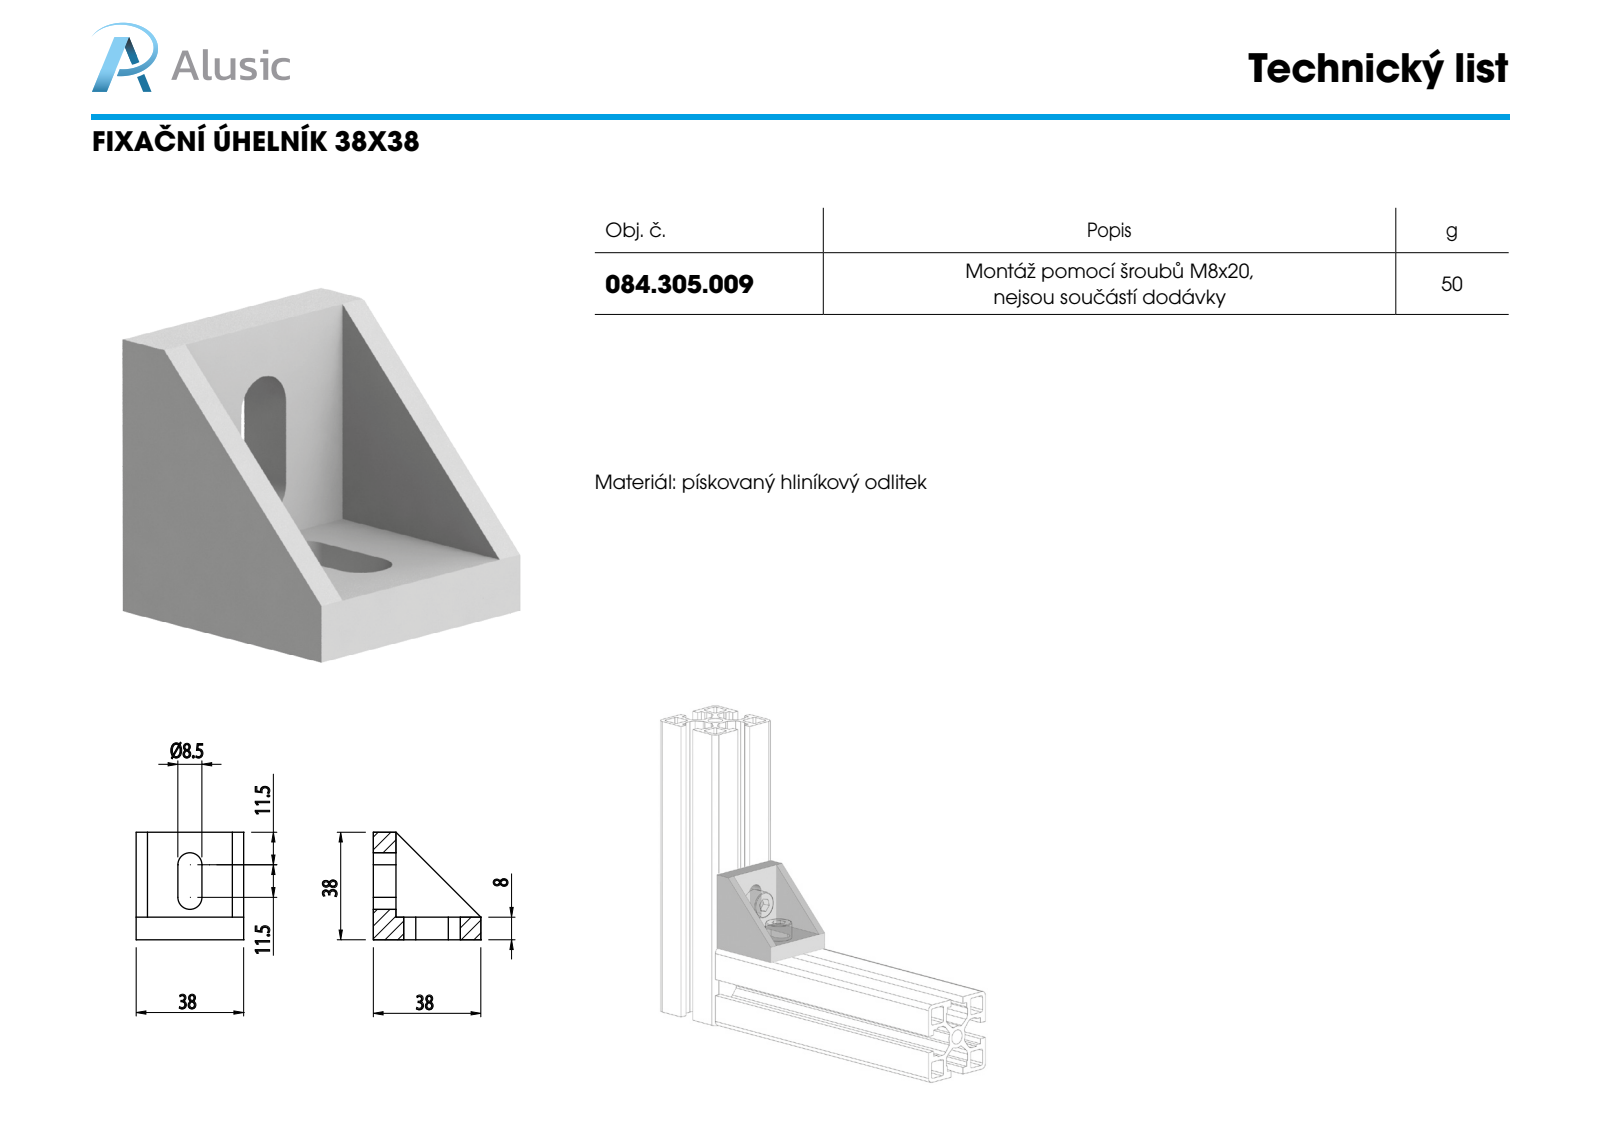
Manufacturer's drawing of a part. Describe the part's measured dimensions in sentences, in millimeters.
The part is named "084.305.009". Its 3-D file was written by "SolidWorks 2011 (CONFIG_CONTROL_DESIGN)". It is 1 solid with 22 faces: 16 planar, 6 cylindrical and 0 other. Overall it measures 38 by 38 by 38 millimeters. Its volume is 21 800 cubic millimeters and its surface area 8 701 square millimeters. Partial cylindrical surfaces (rounded edges, fillets, slot ends): 4 of radius 4.25. The main face-to-face distances are 38, 8, 30, 4, 34, 14.75, 23.25, 10.75, 19.25, 8.5.
